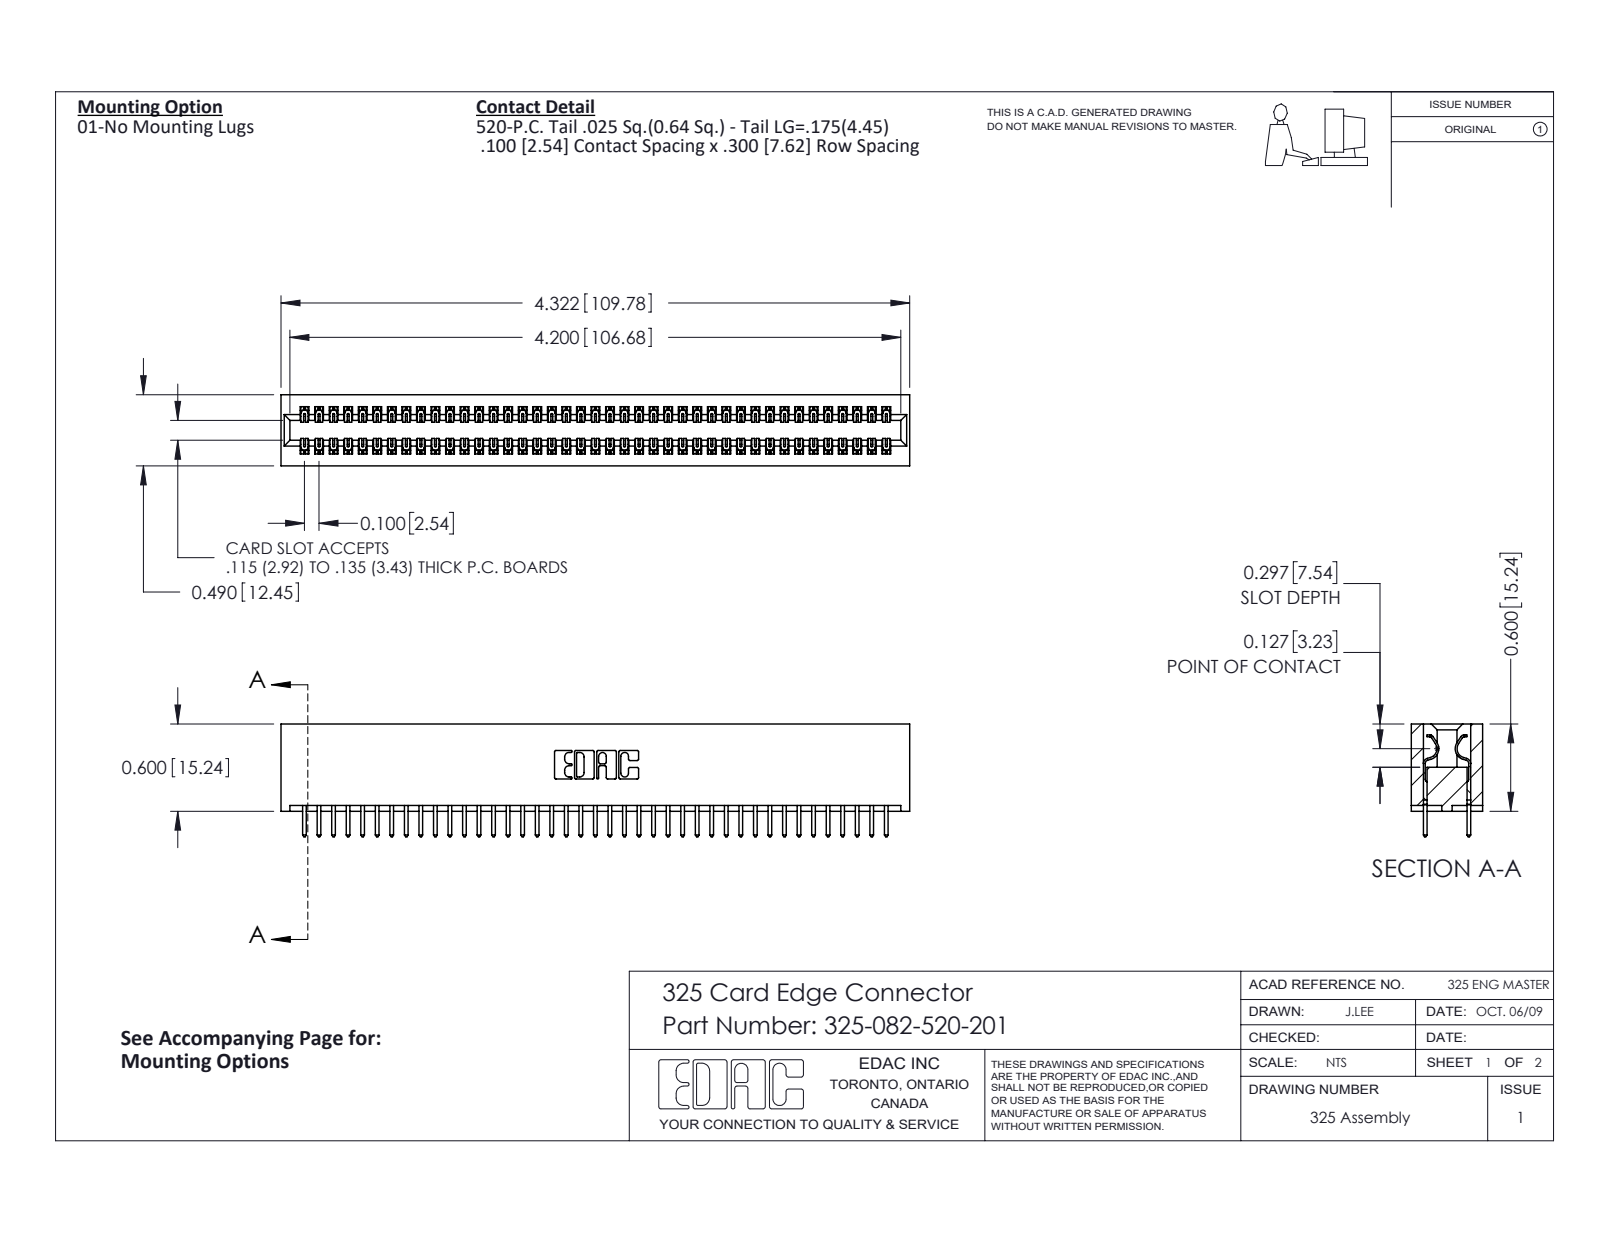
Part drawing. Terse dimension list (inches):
name: 325 Part_Lugless; 325-292-001_325-293-120; 325-082-520-201
written by: SolidWorks 2016 (CONFIG_CONTROL_DESIGN)
unit: in
bodies: 83 solids, 4370 faces (3018 planar, 1352 cylindrical, 0 other)
size: 4.322 × 0.775 × 0.49
volume: 0.901 in³; area: 28.42 in²
rounds: 123× R0.006, 82× R0.01, 22× R0.01, 6× R0.007, 6× R0.031, 3× R0.026, 2× R0.014, 2× R0.022
face distances: 0.083, 0.407, 0.3, 0.49, 0.107, 0.383, 0.025, 0.325, 0.275, 0.56
